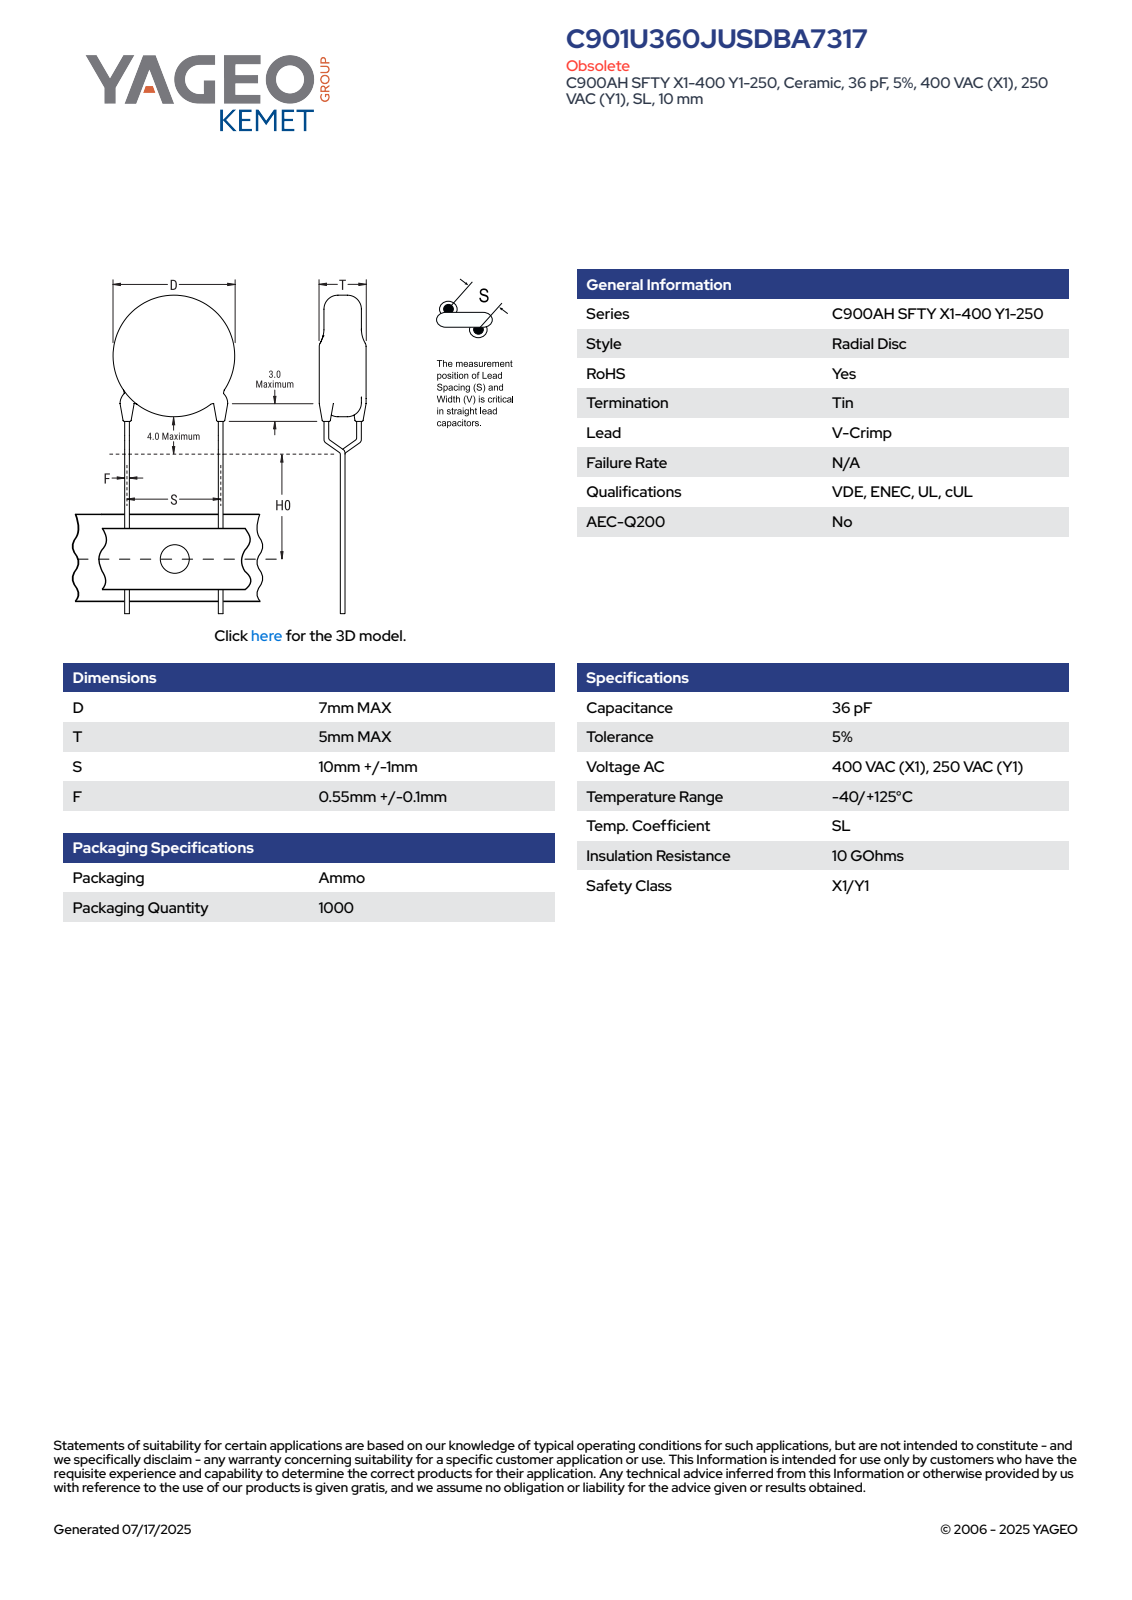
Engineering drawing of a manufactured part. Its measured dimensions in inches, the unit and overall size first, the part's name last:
Units: inches
Overall size (bounding box): 1.213 × 0.419 × 0.197
Round bosses / shafts (diameter × count): ⌀0.026 ×6, ⌀0.276 ×1
Main face-to-face distances: 0.197, 0.902, 0.036, 1.093, 0.191, 1.057, 0.155, 0.146, 0.013, 0.074
Volume: 0.013 in³ · Surface area: 0.448 in²
Bodies: 5 solids, 93 faces (65 planar, 16 cylindrical, 12 other)
Part name (STEP PRODUCT): CCD_VCC900_D7T5S10LL20F0.65
STEP written by: SolidWorks 2014 (AUTOMOTIVE_DESIGN)
